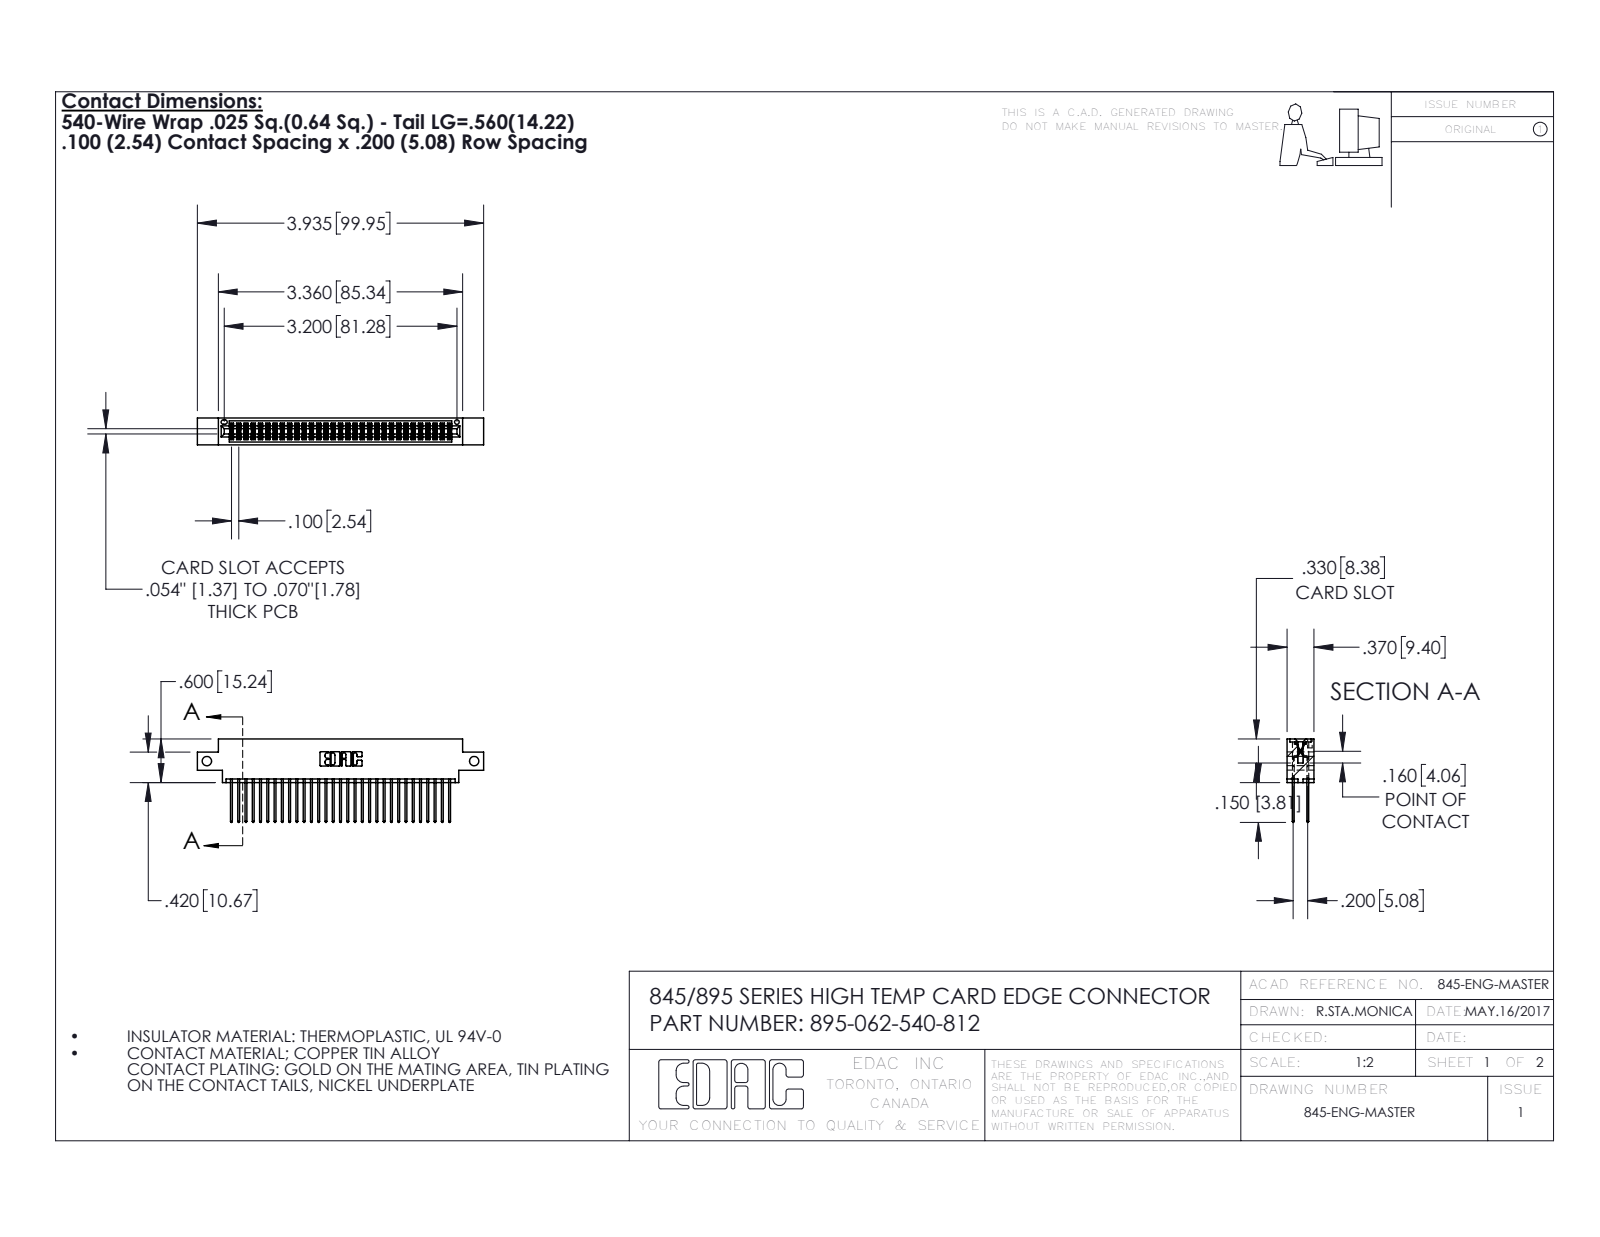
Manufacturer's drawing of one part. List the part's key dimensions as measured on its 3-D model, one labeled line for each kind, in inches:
Part name (STEP PRODUCT): 345-292-001_345-293-140; 345 Part_0.170 Offset - Side Mount; 395-062-540-812
STEP written by: SolidWorks 2016 (CONFIG_CONTROL_DESIGN)
Units: inches
Bodies: 63 solids, 3230 faces (2130 planar, 1100 cylindrical, 0 other)
Overall size (bounding box): 3.935 × 1.147 × 0.37
Volume: 0.588 in³ · Surface area: 23.46 in²
Round holes (diameter × count): ⌀0.128 ×2, ⌀0.064 ×1
Partial cylindrical surfaces — rounded edges, fillets, slot ends (radius × count): R0.006 ×93, R0.01 ×62, R0.01 ×22, R0.007 ×6, R0.031 ×6, R0.026 ×3, R0.014 ×2, R0.019 ×2
Main face-to-face distances: 0.072, 0.298, 0.2, 0.098, 0.272, 0.025, 0.37, 0.225, 0.175, 0.149
Hole centre spacings: 3.675
